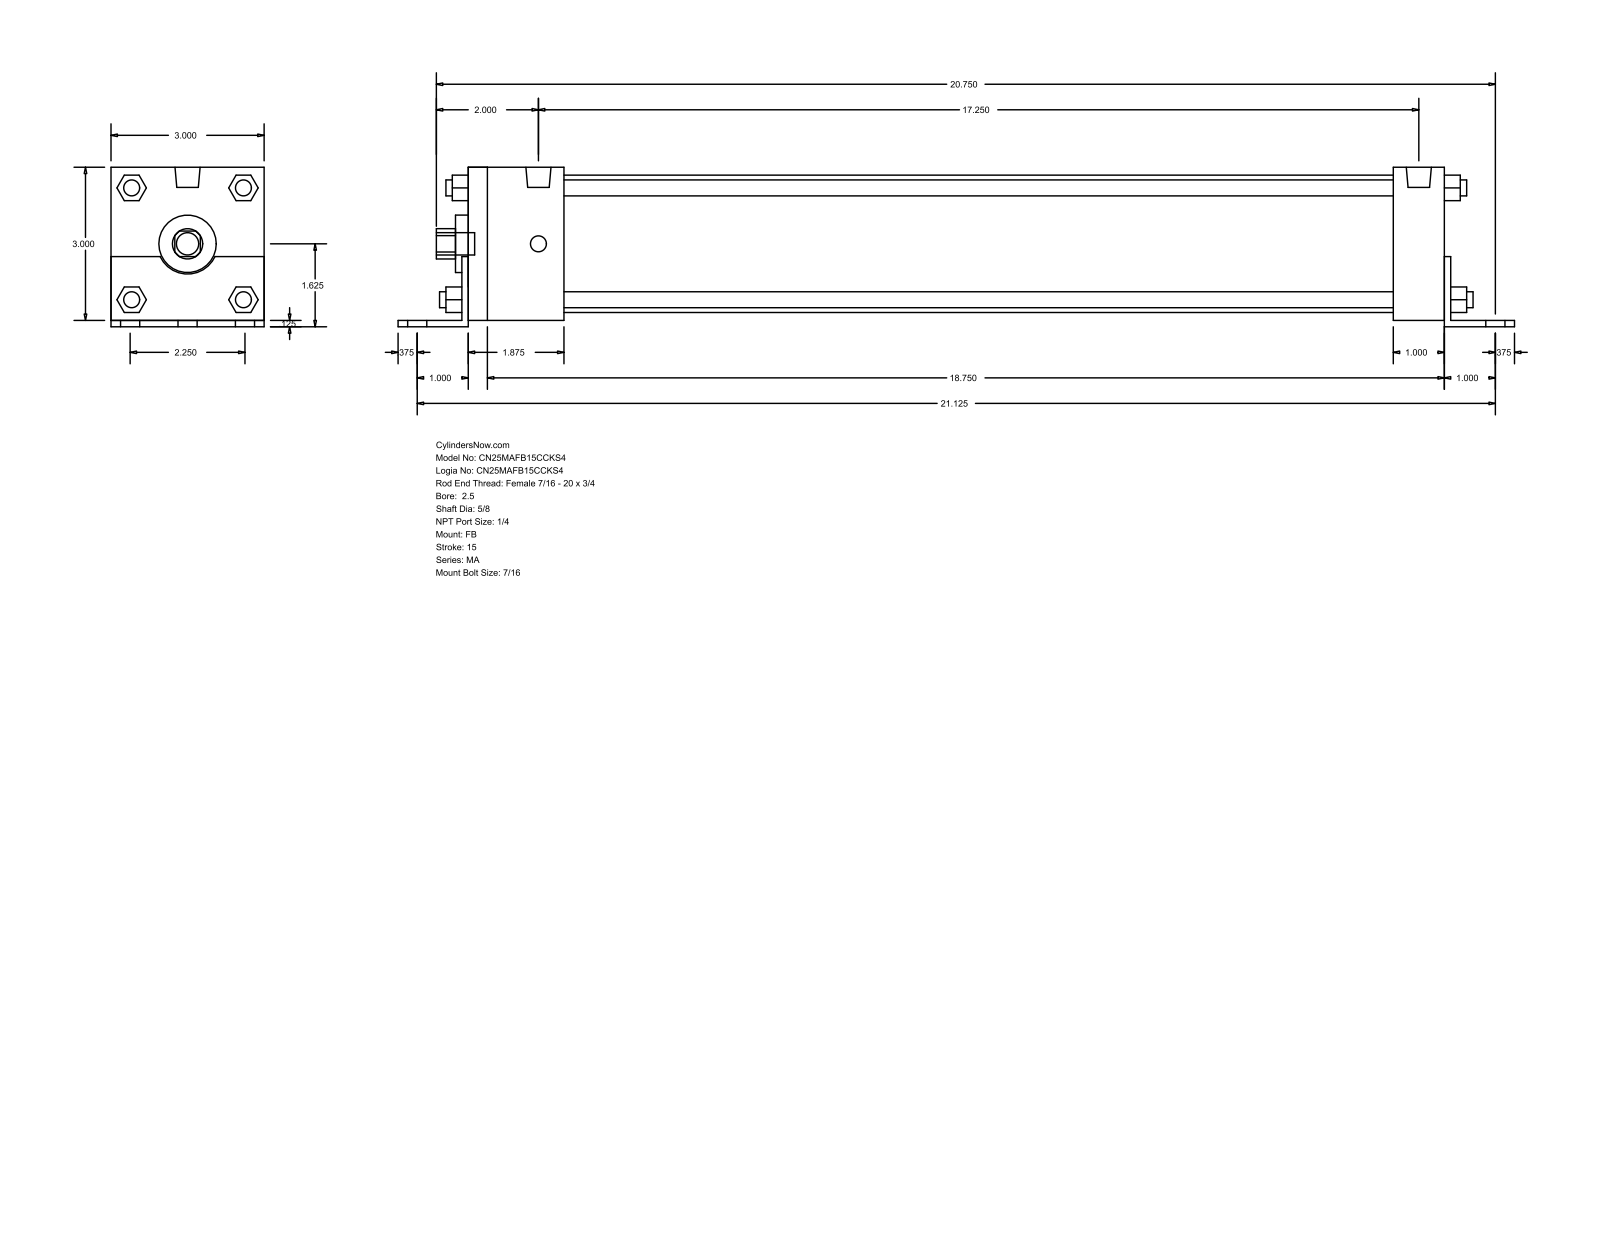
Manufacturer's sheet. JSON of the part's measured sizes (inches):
{"part_name": "MA_FB__0250_0.625", "step_written_by": "GSSL Pune (CONFIG_CONTROL_DESIGN)", "units": "inches", "bodies": {"solids": 0, "faces": 140, "planar": 105, "cylindrical": 35, "other": 0}, "overall_size": [21.875, 3.125, 3], "round_holes": [[0.625, 1], [1.125, 1], [2.69, 1]], "round_bosses_or_shafts": [[0.313, 8], [0.437, 7], [0.492, 2]], "partial_cylinders_radius": [[0.297, 1], [0.593, 1]], "face_to_face_distances": [3, 0.125, 3.125, 19.125, 19.375, 0.125, 19.25, 1.875, 1, 19.25]}
